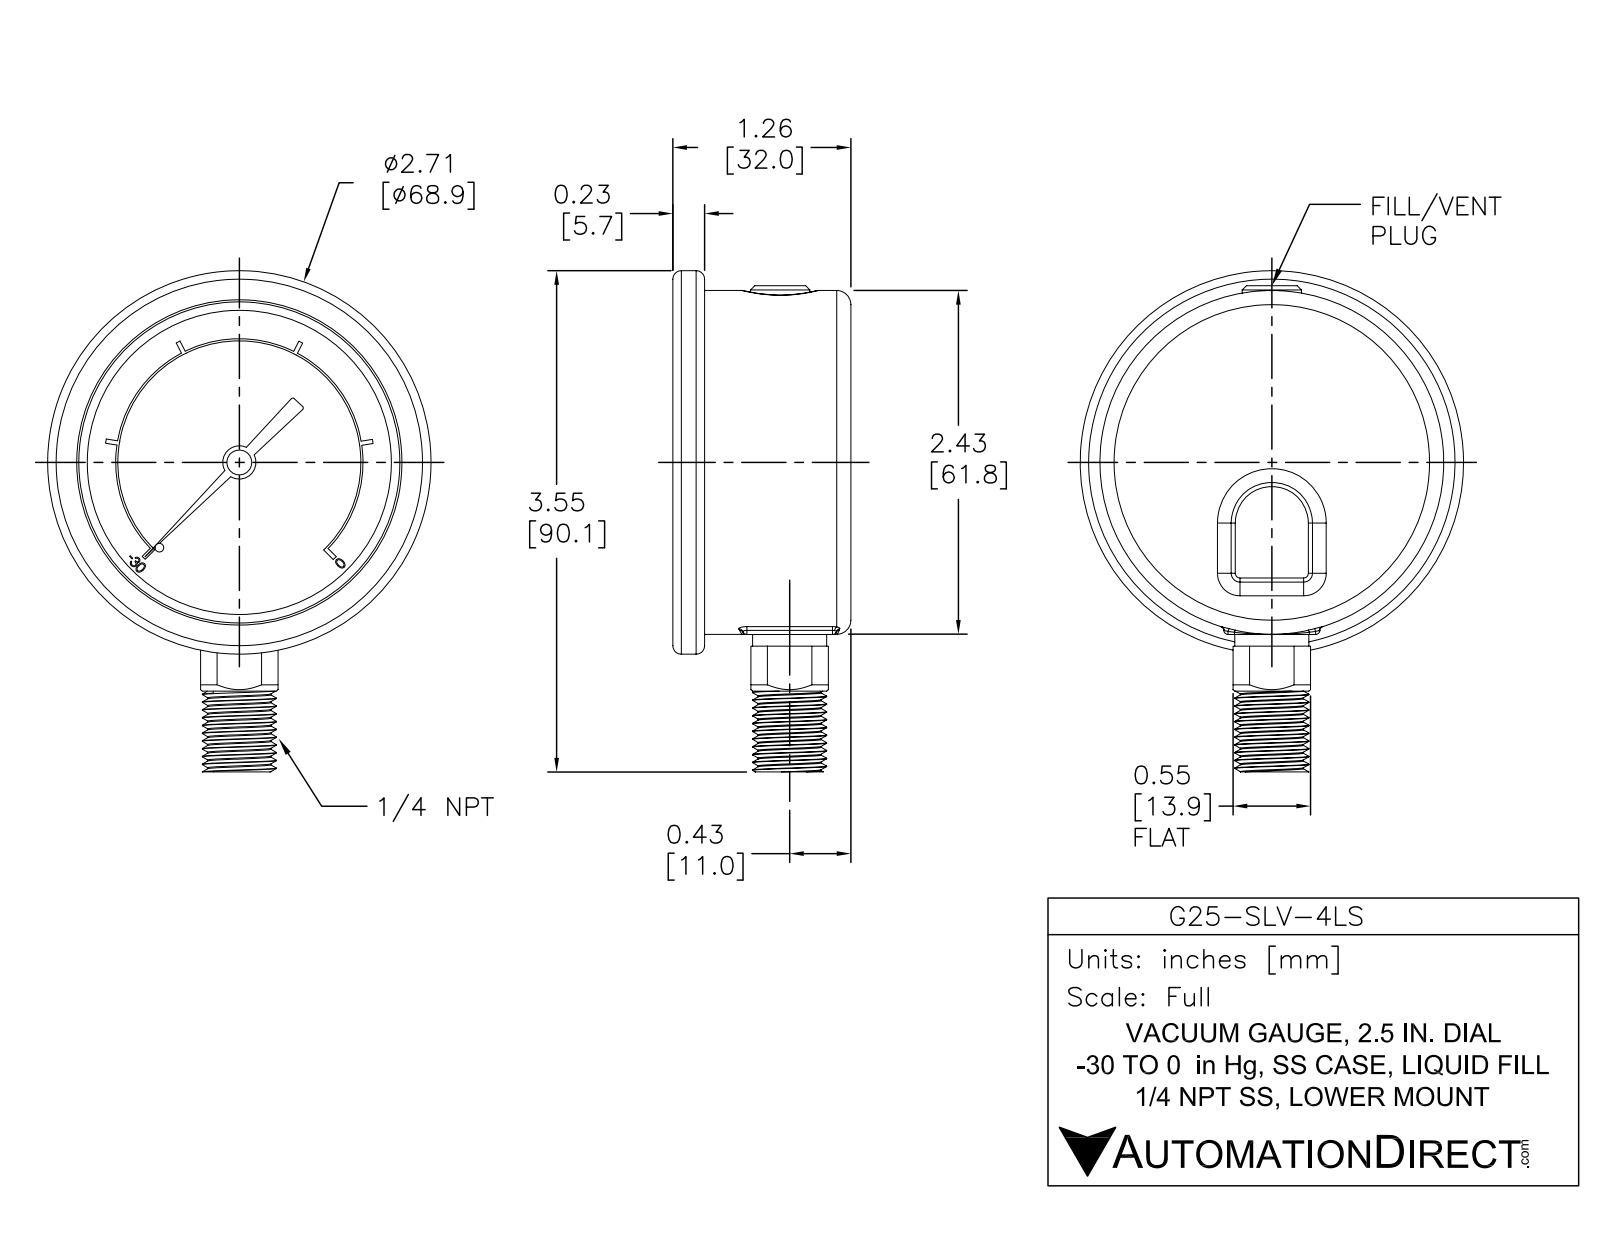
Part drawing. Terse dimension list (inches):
name: G25-SLV-4LS
written by: SolidWorks 2021 (AUTOMOTIVE_DESIGN)
unit: in
bodies: 1 solid, 347 faces (195 planar, 85 cylindrical, 67 other)
size: 3.546 × 2.713 × 1.26
volume: 5.273 in³; area: 24.68 in²
holes: 1× ⌀0.027, 1× ⌀0.071, 1× ⌀0.119, 1× ⌀2.272
bosses: 1× ⌀2.713, 1× ⌀2.433, 1× ⌀0.524, 1× ⌀0.42, 1× ⌀0.235, 1× ⌀0.176, 1× ⌀0.14, 1× ⌀0.041
rounds: 9× R0.03, 3× R0.1, 2× R0.015, 1× R0.316, 1× R0.86, 1× R0.875
face distances: 1.01, 1.26, 0.25, 1.035, 0.025, 0.225, 0.1, 0.91, 0.935, 1.16
hole spacings: 0.067
